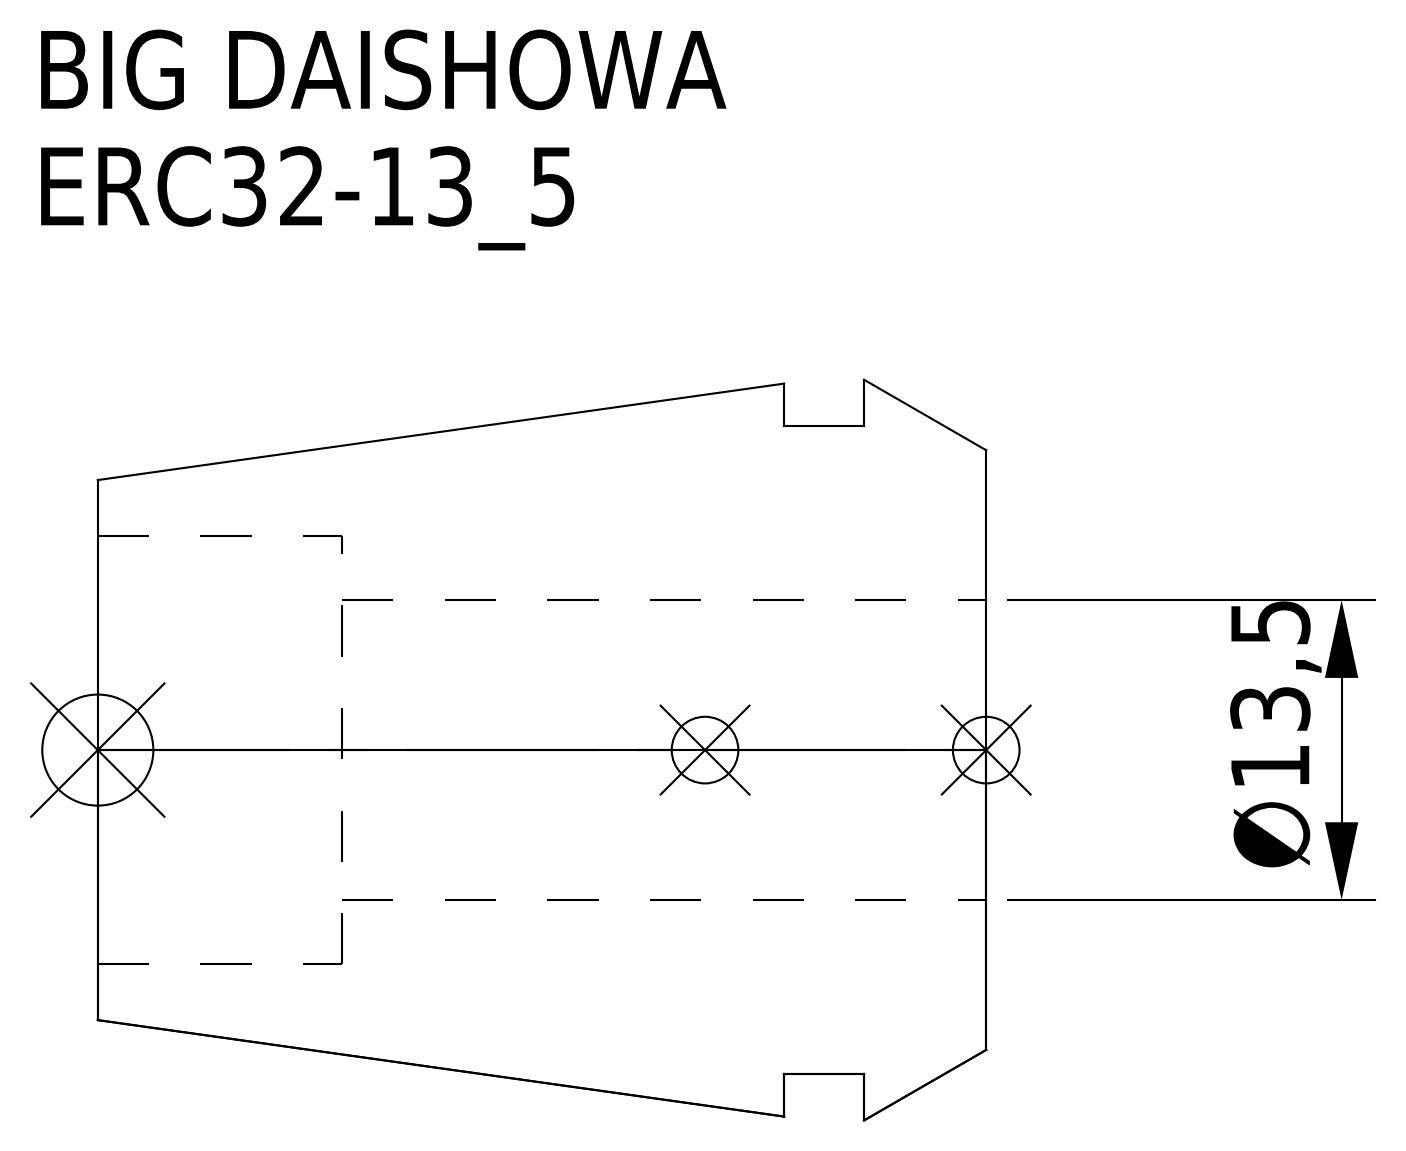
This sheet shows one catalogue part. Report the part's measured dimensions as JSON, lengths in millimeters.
{"part_name": "ERC32-13_5", "step_written_by": "CREO PARAMETRIC BY PTC INC, 2016380 (AUTOMOTIVE_DESIGN)", "units": "millimeters", "bodies": {"solids": 1, "faces": 15, "planar": 5, "cylindrical": 6, "other": 4}, "overall_size": [40, 33.35, 33.35], "volume_mm3": 19073, "surface_area_mm2": 6779, "round_holes": [[13.5, 1], [19.3, 1]], "round_bosses_or_shafts": [[29.2, 1]], "face_to_face_distances": [5.5, 9.1, 3.6, 40, 34.5, 30.9, 29, 23.5, 19.9, 11]}
